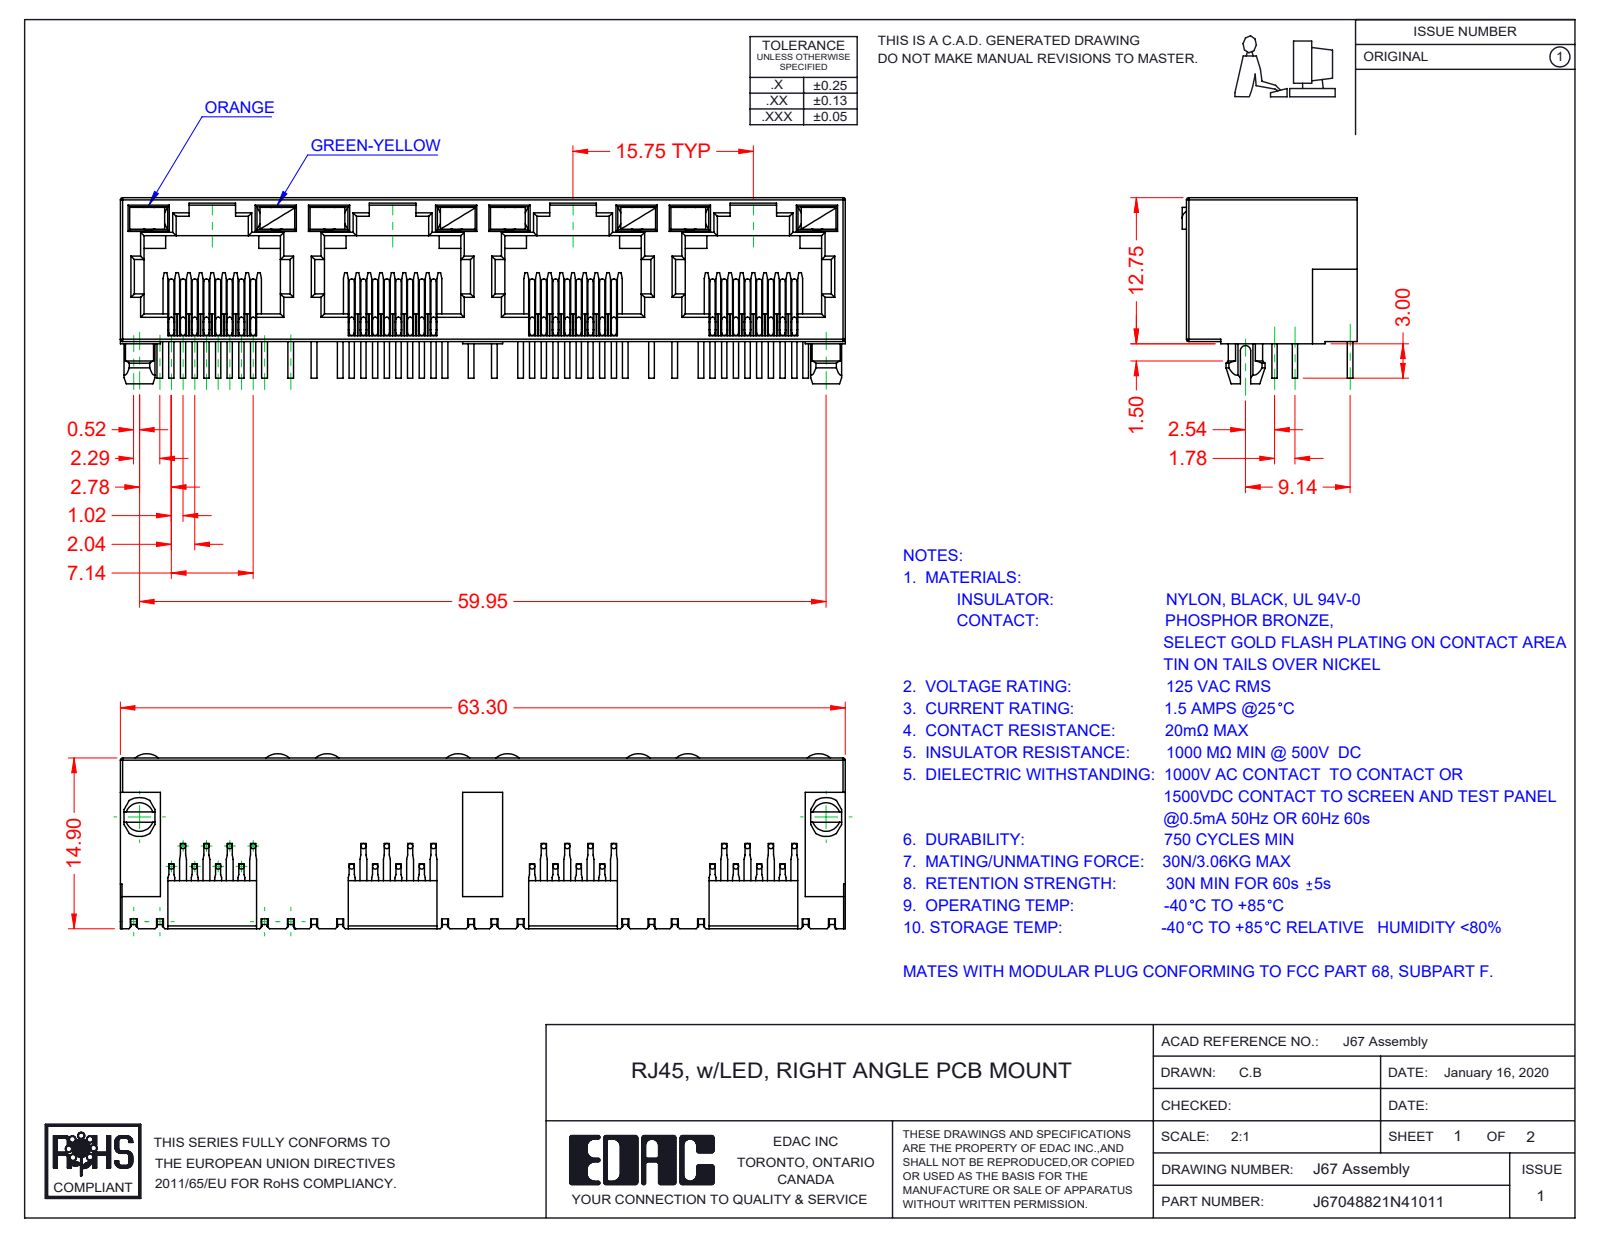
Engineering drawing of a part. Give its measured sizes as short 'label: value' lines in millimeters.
name: 67 Insulator; 67 LED RH_5-Green-Yellow; 67 LED LH_4-Orange; 67 Contacts (+1 more)
written by: SolidWorks 2016 (CONFIG_CONTROL_DESIGN)
unit: mm
bodies: 41 solids, 2473 faces (1781 planar, 484 cylindrical, 208 other)
size: 63.3 × 16.25 × 15.28
volume: 5 159 mm³; area: 11 573 mm²
bosses: 96× ⌀0.46
rounds: 66× R0.2, 29× R0.3, 9× R0.45, 8× R1.55, 2× R1.5, 2× R1.7, 1× R0.35, 1× R1
face distances: 0.5, 12.55, 1.89, 0.89, 10, 15.75, 1, 1.39, 11, 11.89
